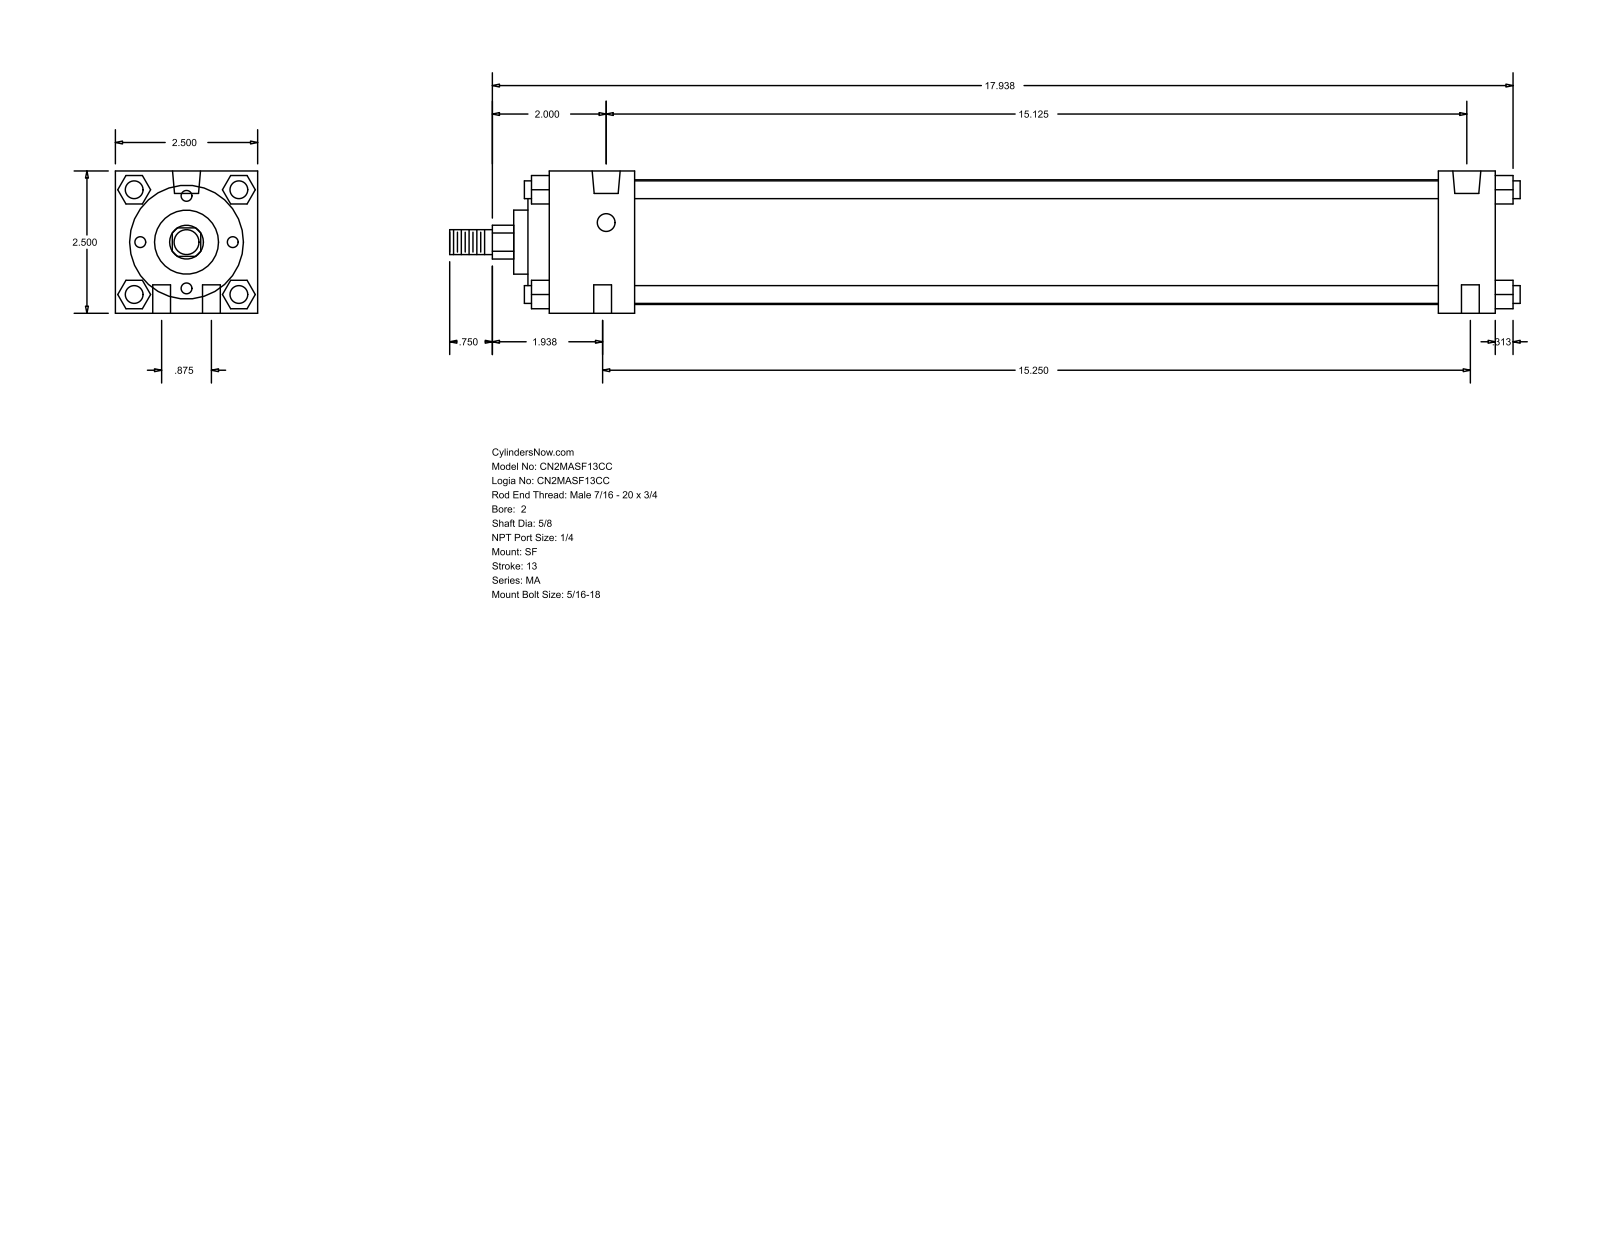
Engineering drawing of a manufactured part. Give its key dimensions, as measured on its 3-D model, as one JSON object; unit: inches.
{"part_name": "MA_SF__0200_0.625", "step_written_by": "GSSL Pune (CONFIG_CONTROL_DESIGN)", "units": "inches", "bodies": {"solids": 0, "faces": 126, "planar": 95, "cylindrical": 31, "other": 0}, "overall_size": [18.813, 2.5, 2.5], "round_holes": [[0.313, 6], [0.492, 2]], "round_bosses_or_shafts": [[0.313, 4], [2.19, 1], [2, 1], [1.125, 1], [0.625, 1], [0.437, 1]], "partial_cylinders_radius": [[0.297, 1]], "face_to_face_distances": [2.5, 0.5, 1.5, 16.625, 15.625, 1, 14.125, 15.125, 0.375, 1.875], "hole_center_spacings": [0.442, 0.875, 15.125, 15.194, 15.194, 15.25, 15.275]}
